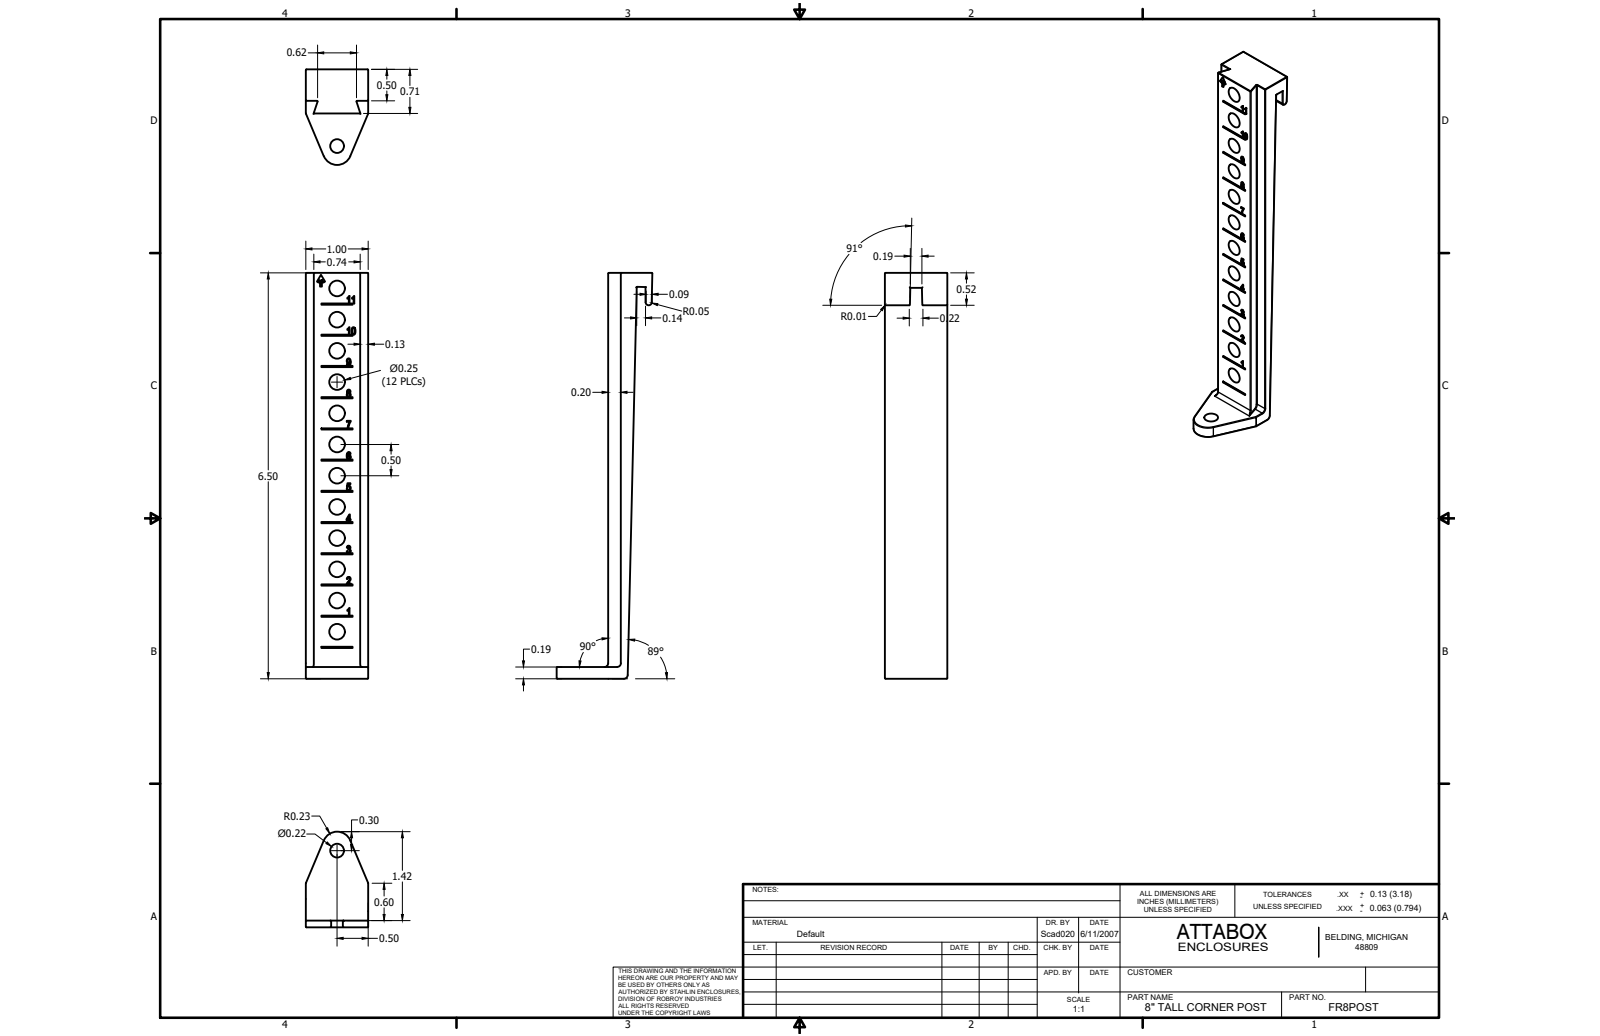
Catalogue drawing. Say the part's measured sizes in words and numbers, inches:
The part is named "FR8POST". Its 3-D file was written by "SolidWorks 2019 (AUTOMOTIVE_DESIGN)". It is 12 solids with 1552 faces: 804 planar, 256 cylindrical and 492 other. Overall it measures 14.688 by 12.688 by 6.703 inches. Its volume is 8.636 cubic inches and its surface area 104.7 square inches. Round holes: 48 of diameter 0.25, 4 of diameter 0.217, 4 of diameter 0.22. Round bosses or shafts: 4 of diameter 0.433, 4 of diameter 0.373, 4 of diameter 0.19. Partial cylindrical surfaces (rounded edges, fillets, slot ends): 156 of radius 0.01, 16 of radius 0.06, 4 of radius 0.049, 4 of radius 0.23. The main face-to-face distances are 0.203, 17.154, 16.951, 1, 1.414, 8.472, 8.886, 8.269, 8.683, 7.472. The hole center spacings are 1.5, 0.5, 1, 1.732, 2.061, 2, 2.45, 2.5.
